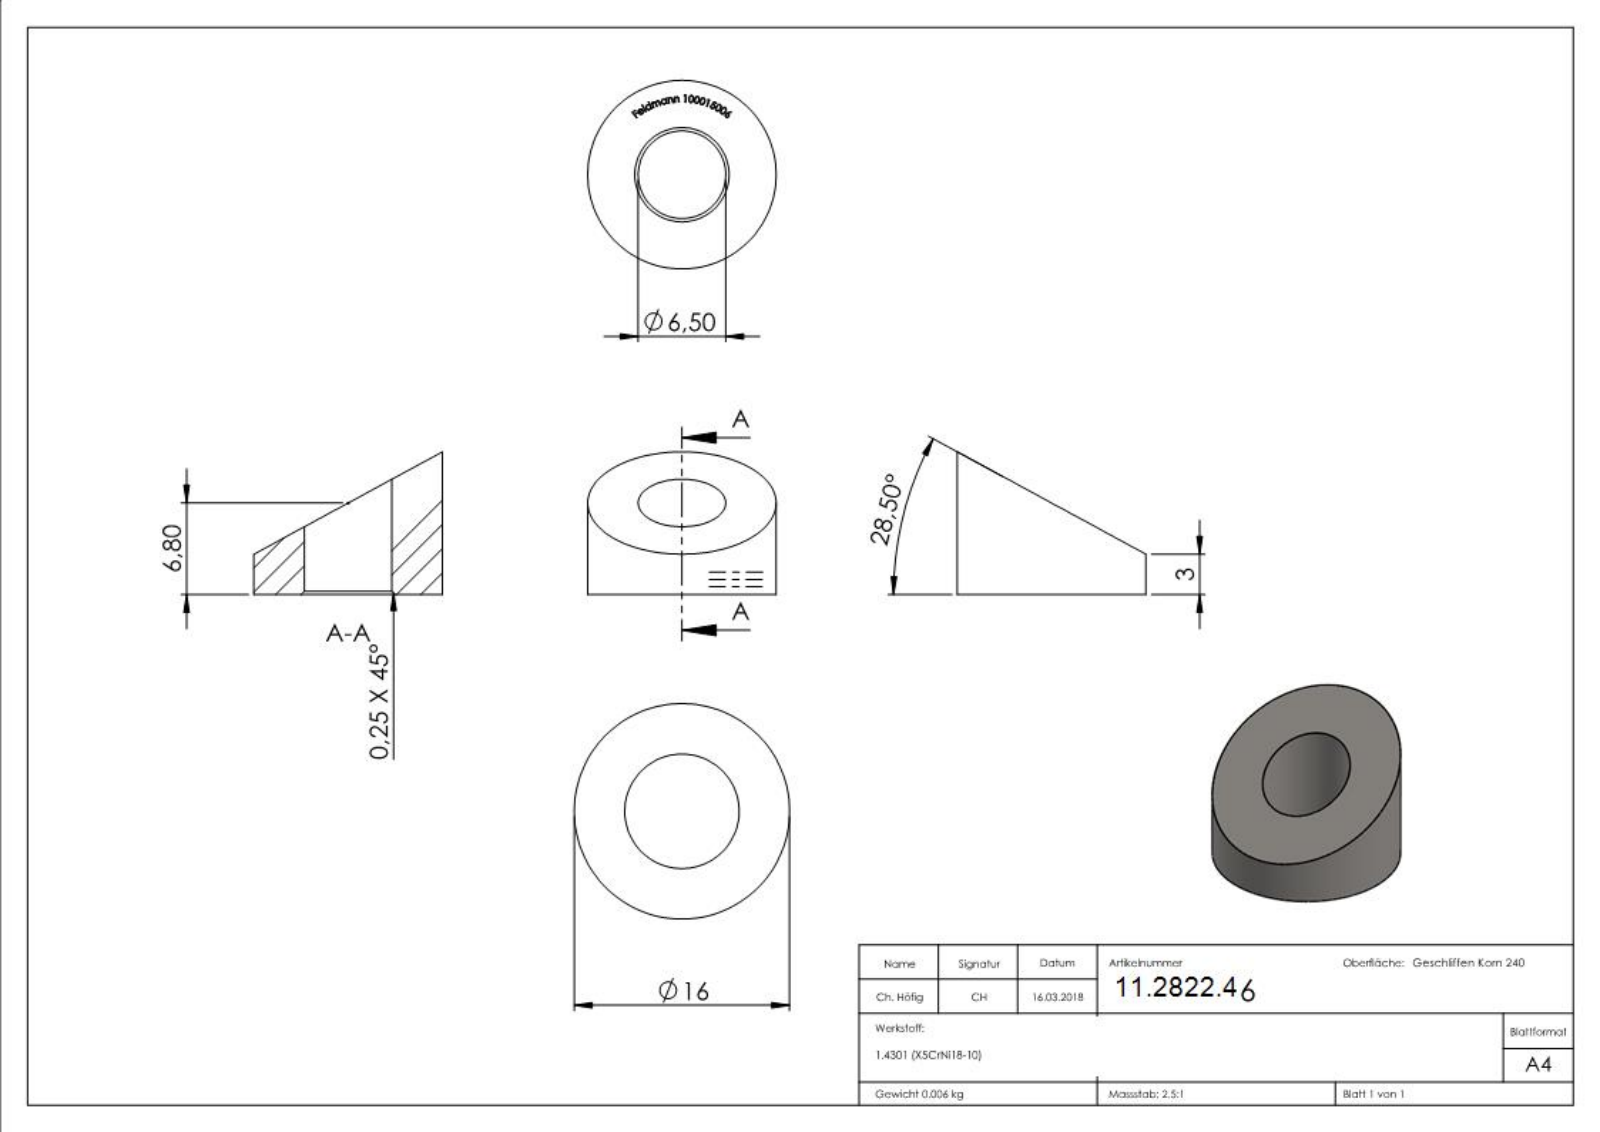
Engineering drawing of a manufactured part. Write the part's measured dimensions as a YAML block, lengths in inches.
part_name: "100015006"
step_written_by: "SolidWorks 2015 (CONFIG_CONTROL_DESIGN)"
units: inches
bodies: {solids: 1, faces: 219, planar: 103, cylindrical: 4, other: 112}
overall_size: [0.551, 0.551, 0.417]
volume: 0.05
surface_area: 1.08
round_holes:
  - {diameter: 0.256, count: 1}
round_bosses_or_shafts:
  - {diameter: 0.551, count: 1}
face_to_face_distances: [0.021, 0.013, 0.019, 0.012, 0.023, 0.015, 0.013, 0.019, 0.021, 0.014]
